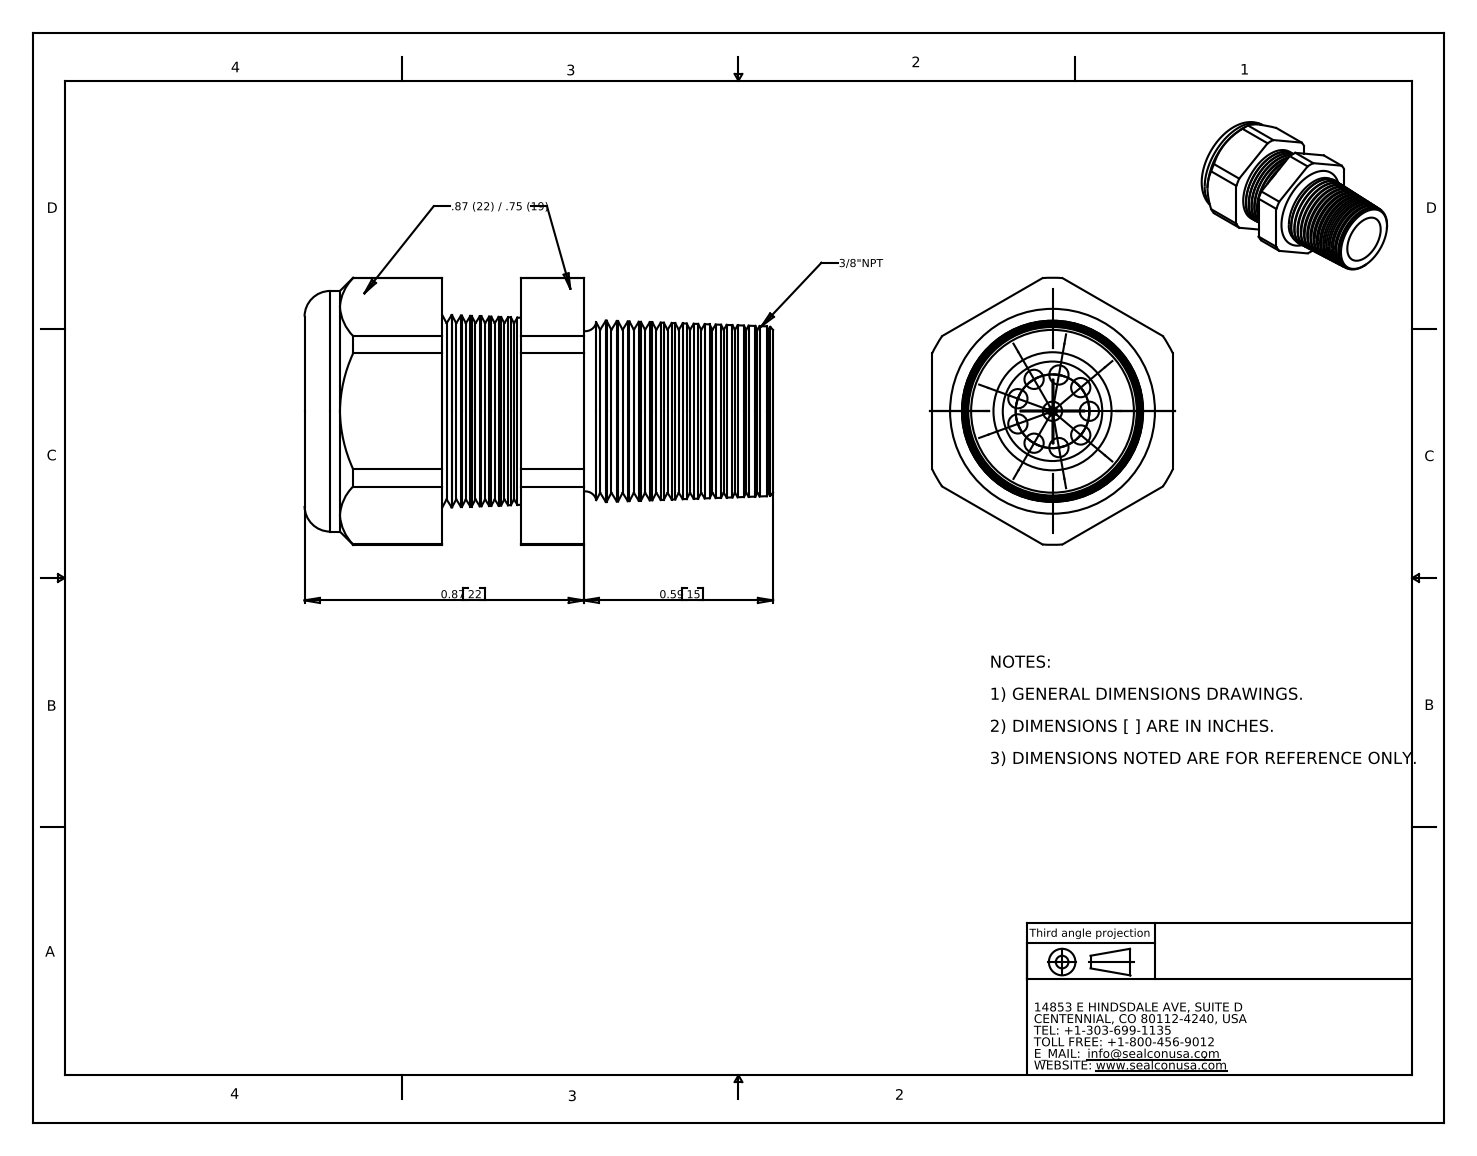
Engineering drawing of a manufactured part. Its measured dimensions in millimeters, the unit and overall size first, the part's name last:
Units: millimetres
Overall size (bounding box): 37.1 × 21.2 × 19.1
Round holes (diameter × count): ⌀1.5 ×10, ⌀7.4 ×1, ⌀7.9 ×1
Round bosses / shafts (diameter × count): ⌀19.1 ×1
Partial cylindrical surfaces — rounded edges, fillets, slot ends (radius × count): R10.6 ×1
Main face-to-face distances: 19.1, 17.1, 10.9, 6.2, 19.1, 22.1, 11.2, 5, 37.1, 26.2
Hole centre spacings: 2.9, 5.1, 3.8, 5.7, 2, 2, 3.8, 2.9
Volume: 6 010 mm³ · Surface area: 4 610 mm²
Bodies: 2 solids, 218 faces (20 planar, 40 cylindrical, 158 other)
Part name (STEP PRODUCT): CD09N5-GY
STEP written by: SolidWorks 2007 (CONFIG_CONTROL_DESIGN)
